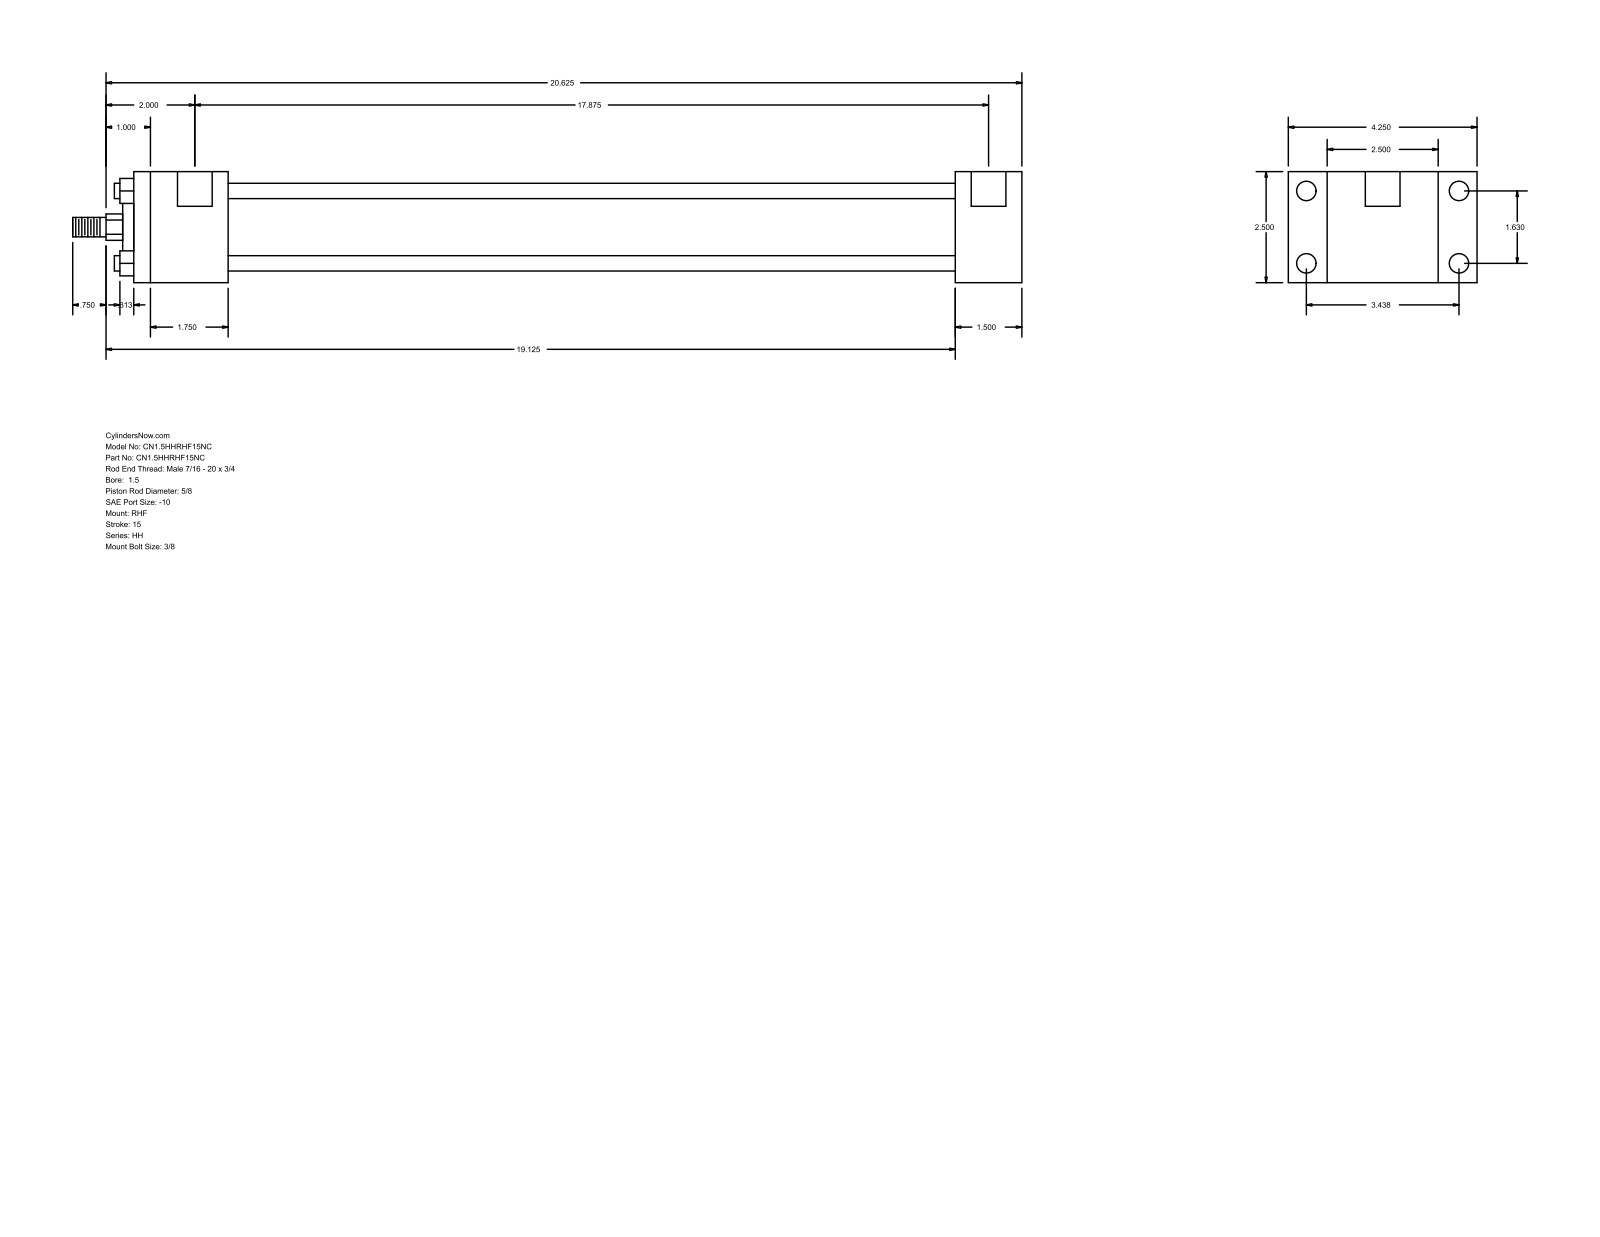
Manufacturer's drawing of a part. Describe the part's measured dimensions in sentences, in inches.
The part is named "HH_RHF__0150_0.625". Its 3-D file was written by "GSSL Pune (CONFIG_CONTROL_DESIGN)". It is 0 solids with 88 faces: 60 planar, 28 cylindrical and 0 other. Overall it measures 21.375 by 4.25 by 2.5 inches. Round holes: 4 of diameter 0.219, 4 of diameter 0.438, 2 of diameter 0.781. Round bosses or shafts: 4 of diameter 0.345, 1 of diameter 1.75, 1 of diameter 1.125, 1 of diameter 0.625, 1 of diameter 0.437. Partial cylindrical surfaces (rounded edges, fillets, slot ends): 1 of radius 0.297. The main face-to-face distances are 2.5, 0.875, 3.375, 1.5, 18.5, 20, 4.25, 2.125, 16.375, 17.875. The hole center spacings are 0.063, 1.63, 3.438, 3.805, 17.937, 18, 17.875.
